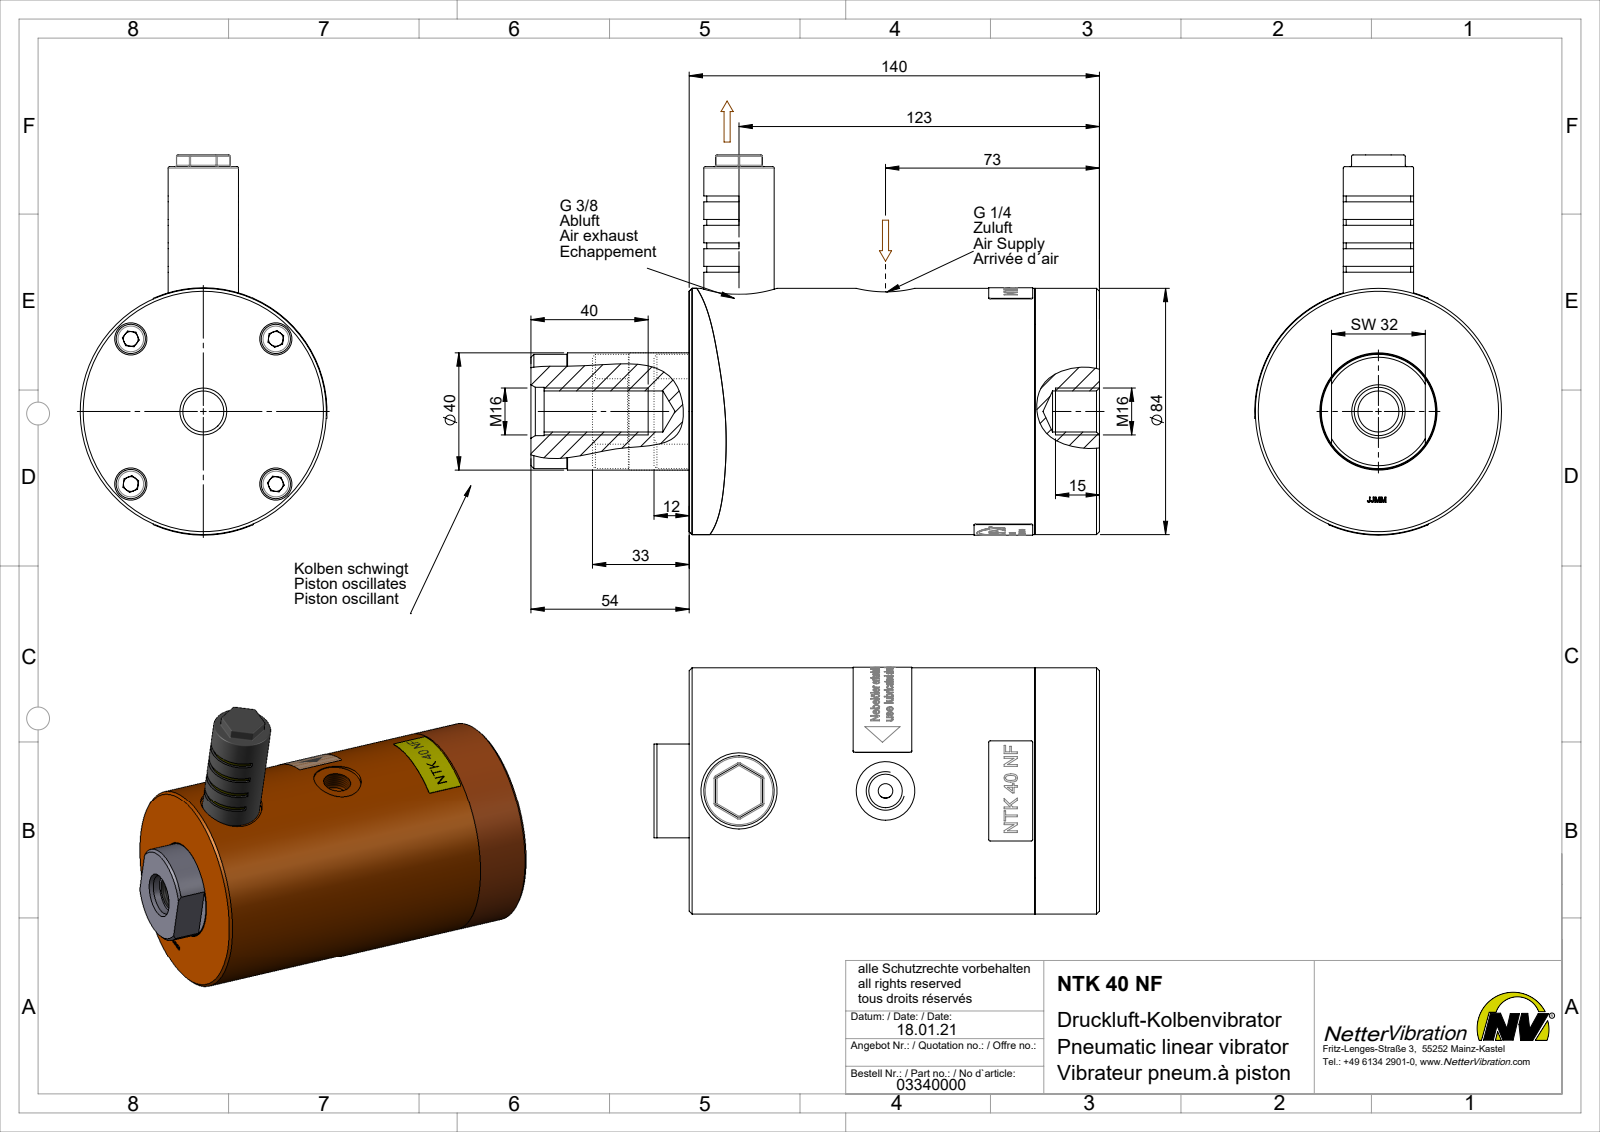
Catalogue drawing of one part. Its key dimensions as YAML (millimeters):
part_name: "NTK 40 NF #03340000"
step_written_by: "SolidWorks 2015 (AUTOMOTIVE_DESIGN)"
units: millimeters
bodies: {solids: 11, faces: 513, planar: 154, cylindrical: 270, other: 89}
overall_size: [152, 129.7, 84.2]
volume: 731949
surface_area: 104451
round_holes:
  - {diameter: 5, count: 5}
  - {diameter: 6.5, count: 4}
  - {diameter: 11, count: 4}
  - {diameter: 11.45, count: 1}
  - {diameter: 14, count: 1}
  - {diameter: 14.95, count: 1}
  - {diameter: 16.5, count: 1}
  - {diameter: 20, count: 1}
  - {diameter: 26, count: 1}
  - {diameter: 40, count: 1}
round_bosses_or_shafts:
  - {diameter: 10, count: 4}
  - {diameter: 6, count: 4}
  - {diameter: 84, count: 1}
  - {diameter: 39, count: 1}
  - {diameter: 24, count: 1}
  - {diameter: 16.66, count: 1}
partial_cylinders:
  - {radius: 0.5, count: 30}
  - {radius: 11, count: 1}
  - {radius: 42.2, count: 1}
face_to_face_distances: [22, 118, 140, 68, 50, 72, 12, 130, 80, 152]
hole_center_spacings: [35, 49.5, 70, 50]
